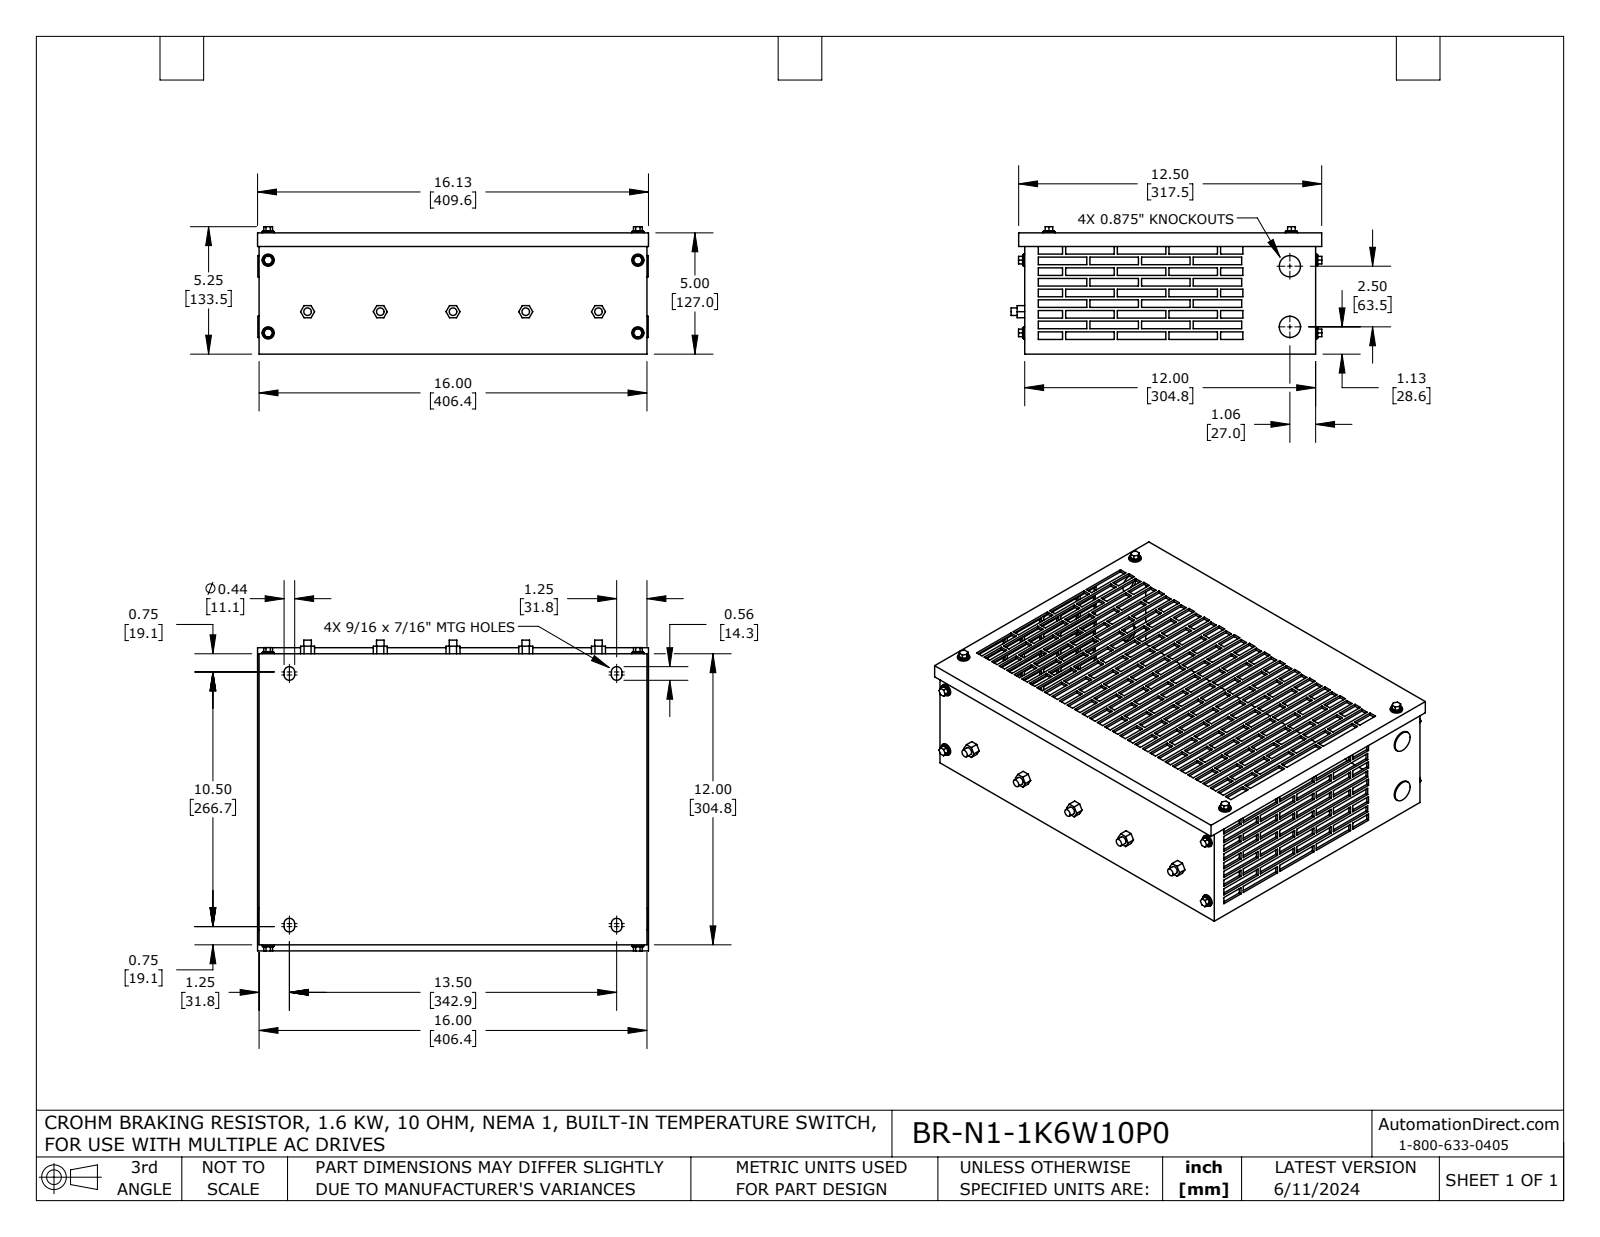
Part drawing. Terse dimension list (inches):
name: BR-N1-1K6W10P0
written by: SolidWorks 2021 (AUTOMOTIVE_DESIGN)
unit: in
bodies: 34 solids, 1255 faces (1149 planar, 106 cylindrical, 0 other)
size: 16.125 × 12.817 × 5.254
volume: 54.77 in³; area: 1 200 in²
holes: 8× ⌀0.25, 2× ⌀0.75
bosses: 8× ⌀0.5, 8× ⌀0.437, 5× ⌀0.313, 2× ⌀0.875
rounds: 8× R0.219
face distances: 0.1, 4.9, 11.9, 5, 4.8, 12, 11.8, 15.9, 16, 0.25
hole spacings: 15.25, 3, 10, 15.543, 18.237, 2.5
